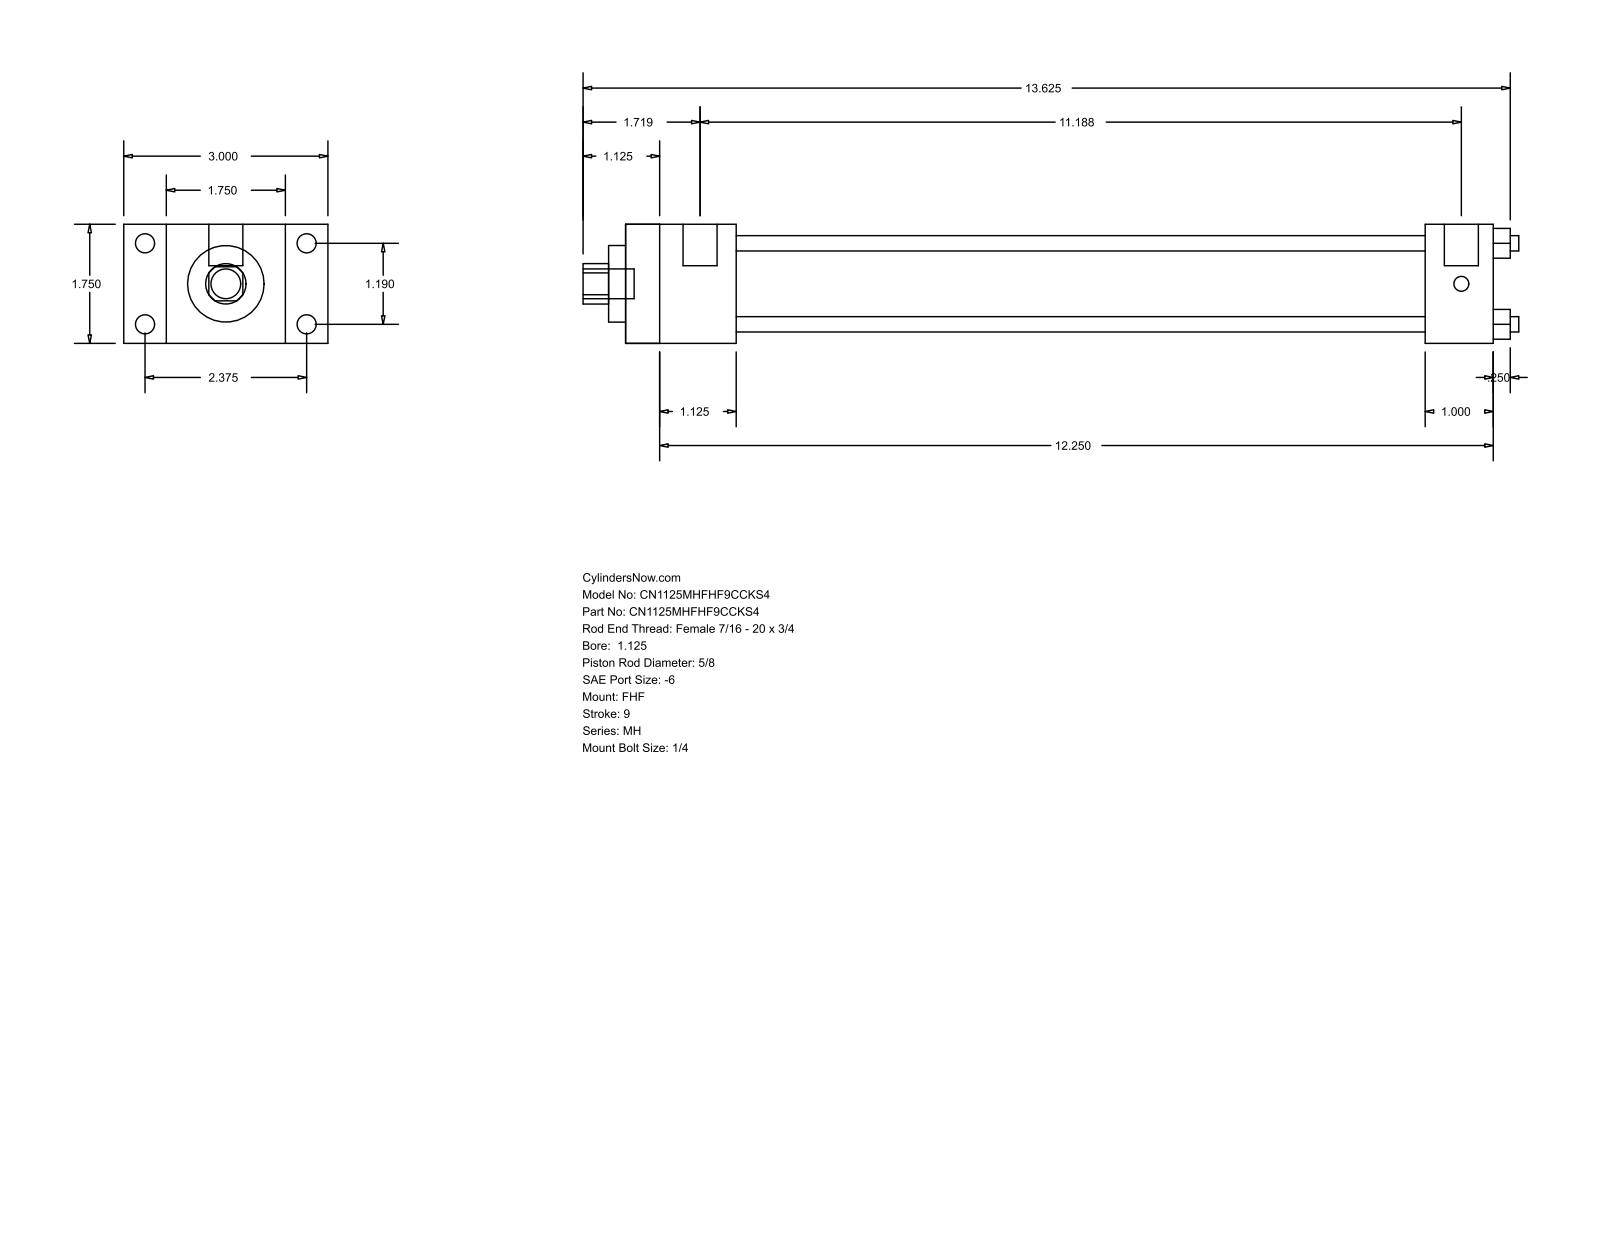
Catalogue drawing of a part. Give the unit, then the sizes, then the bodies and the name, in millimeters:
Units: millimetres
Overall size (bounding box): 349.25 × 76.2 × 44.45
Round holes (diameter × count): ⌀5.71 ×4, ⌀15.88 ×1, ⌀28.57 ×1, ⌀34.92 ×1
Round bosses / shafts (diameter × count): ⌀7.14 ×4, ⌀5.56 ×4, ⌀12.7 ×2, ⌀11.11 ×1
Partial cylindrical surfaces — rounded edges, fillets, slot ends (radius × count): R7.54 ×1
Main face-to-face distances: 44.46, 15.87, 60.33, 41.27, 76.2, 323.85, 282.58, 298.44, 257.17, 25.41
Hole centre spacings: 21.37, 30.22, 42.74
Bodies: 0 solids, 88 faces (60 planar, 28 cylindrical, 0 other)
Part name (STEP PRODUCT): MH_FHF__0112_0.625
STEP written by: GSSL Pune (CONFIG_CONTROL_DESIGN)
